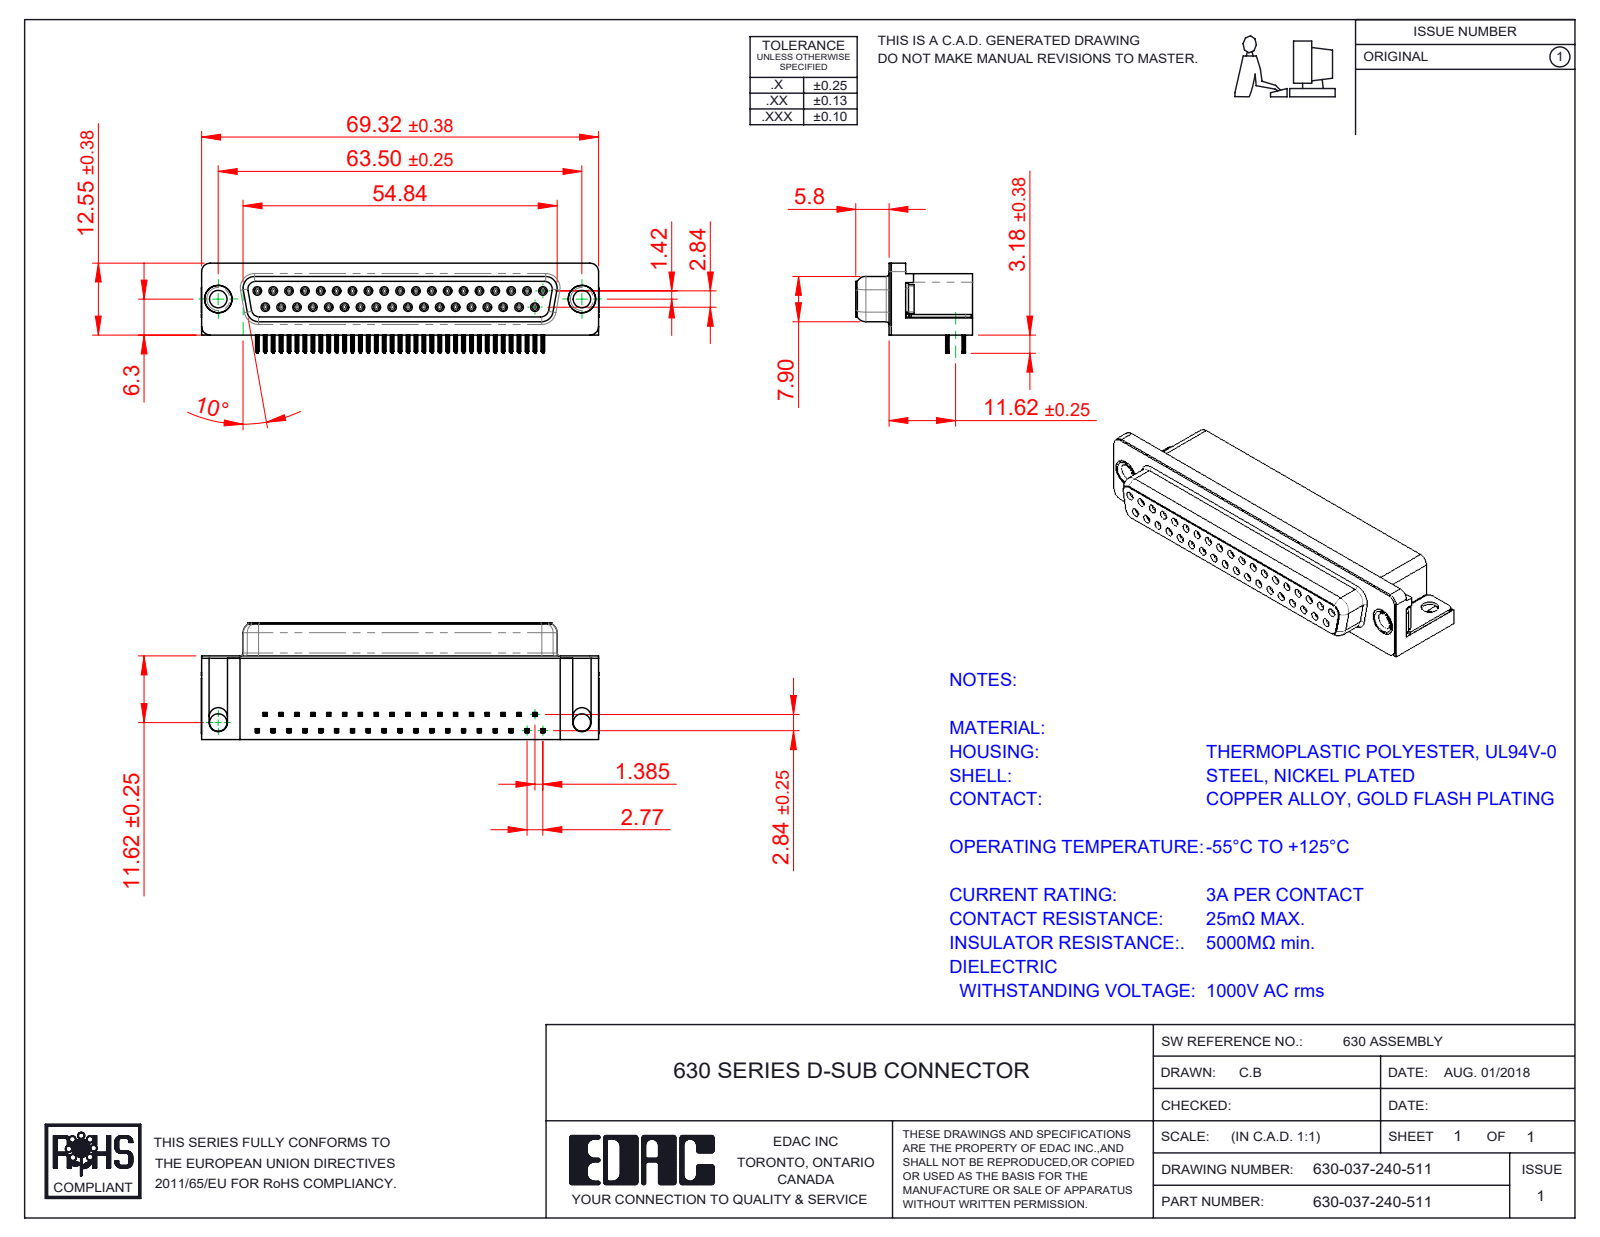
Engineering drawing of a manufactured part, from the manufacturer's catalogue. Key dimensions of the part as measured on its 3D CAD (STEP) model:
Part name (STEP PRODUCT): 630 Thru Hole Board Mount; 630 Shell_37 Socket; 630 Thru Hole Rivet; 630 Contact Bottom (+3 more)
STEP written by: SolidWorks 2020 (CONFIG_CONTROL_DESIGN)
Units: millimetres
Bodies: 43 solids, 5520 faces (2502 planar, 1280 cylindrical, 1738 other)
Overall size (bounding box): 69.4 × 20.4 × 15.73
Volume: 11 801 mm³ · Surface area: 13 511 mm²
Round holes (diameter × count): ⌀0.8 ×37, ⌀0.9 ×37, ⌀3.05 ×4, ⌀4 ×2, ⌀4.8 ×2, ⌀5 ×2
Round bosses / shafts (diameter × count): ⌀1.2 ×37, ⌀4.9 ×2, ⌀4.75 ×2, ⌀3.85 ×2
Partial cylindrical surfaces — rounded edges, fillets, slot ends (radius × count): R0.1 ×296, R0.15 ×148, R0.35 ×74, R0.34 ×37, R0.28 ×18, R1 ×18, R0.25 ×8, R1.35 ×8
Main face-to-face distances: 0.4, 6.2, 10.34, 14.2, 0.85, 6.65, 2.84, 0.45, 14.6, 2.9
Hole centre spacings: 3.16, 2.77, 5.54, 8.31, 11.08, 13.85, 16.62, 19.39
